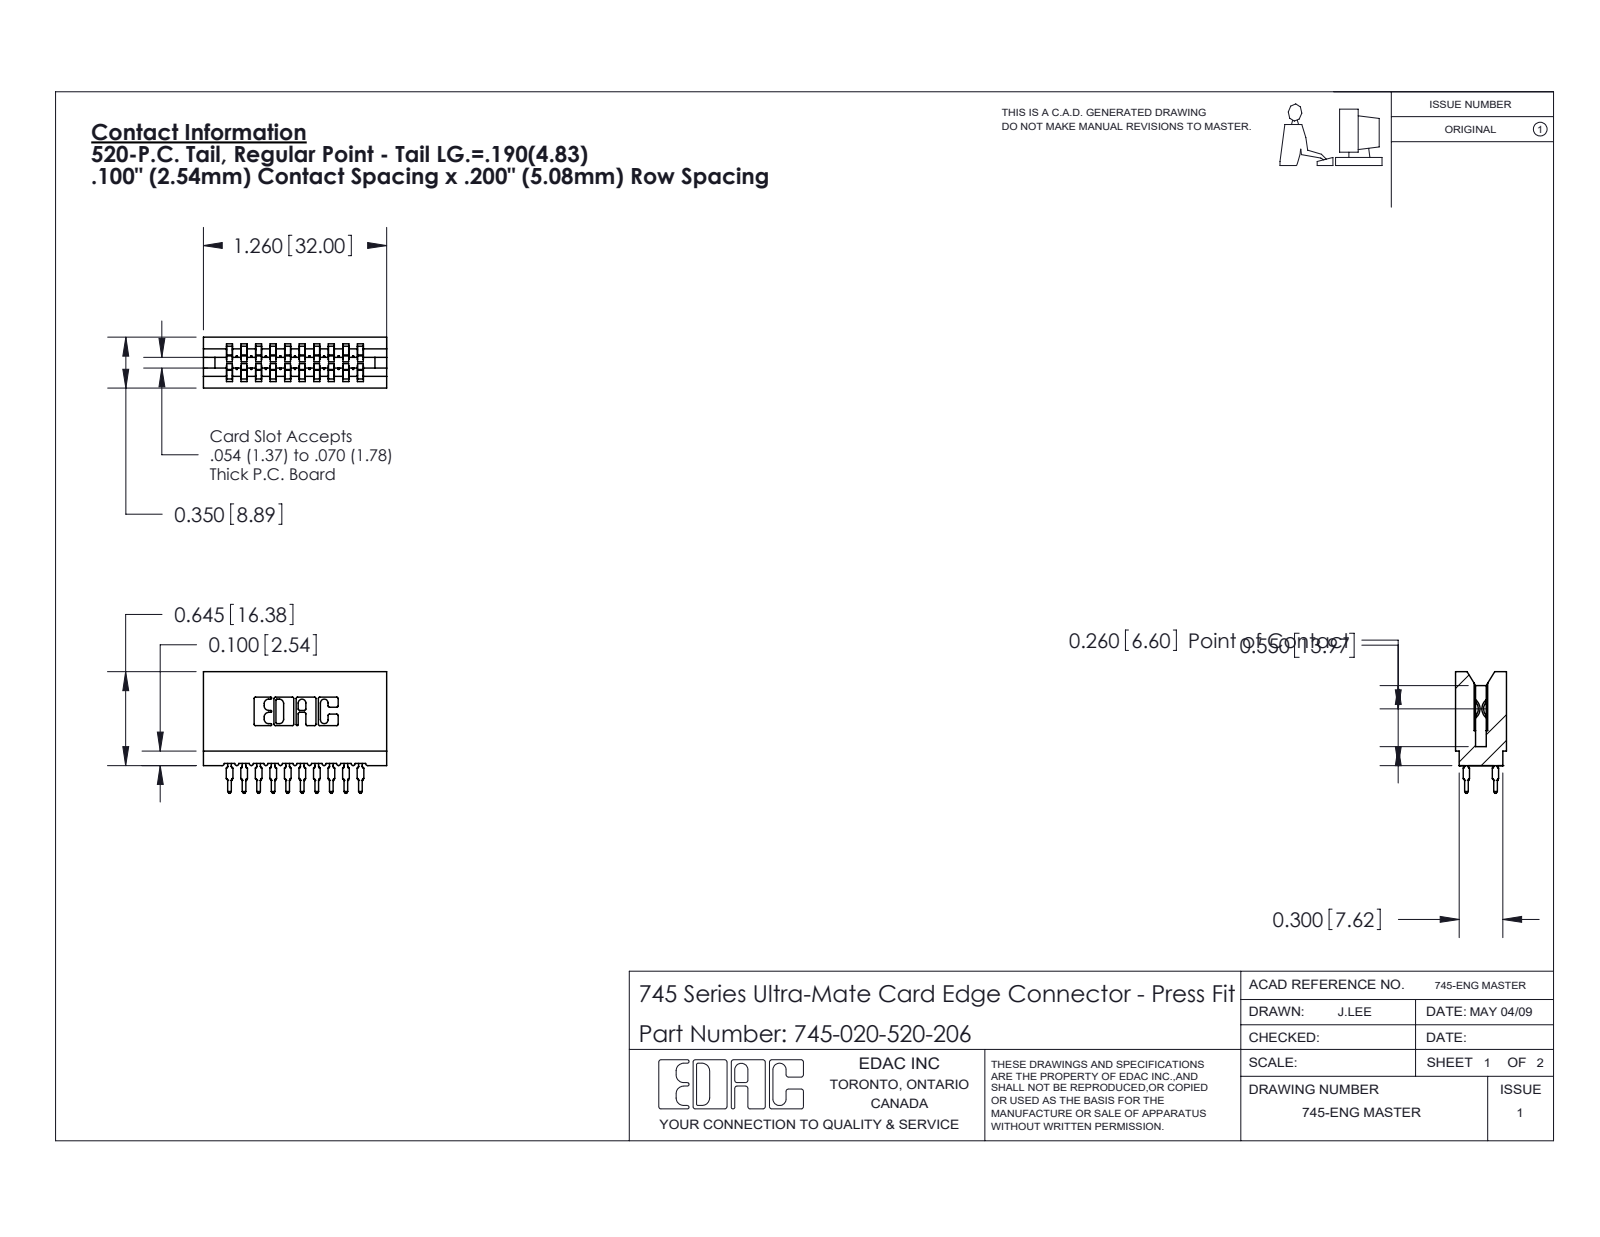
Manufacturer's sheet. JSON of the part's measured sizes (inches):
{"part_name": "745-292-001_520; 745-020-520-206; 745 Part_Insulator Option - 06", "step_written_by": "SolidWorks 2020 (CONFIG_CONTROL_DESIGN)", "units": "inches", "bodies": {"solids": 21, "faces": 1886, "planar": 976, "cylindrical": 390, "other": 520}, "overall_size": [1.26, 0.836, 0.35], "volume_in3": 0.185, "surface_area_in2": 8.318, "partial_cylinders_radius": [[0.021, 40], [0.01, 22], [0.015, 20], [0.005, 8], [0.011, 8], [0.007, 6], [0.031, 6], [0.026, 3]], "face_to_face_distances": [0.1, 0.2, 0.3, 0.4, 0.042, 0.142, 0.5, 0.058, 0.242, 0.158]}
